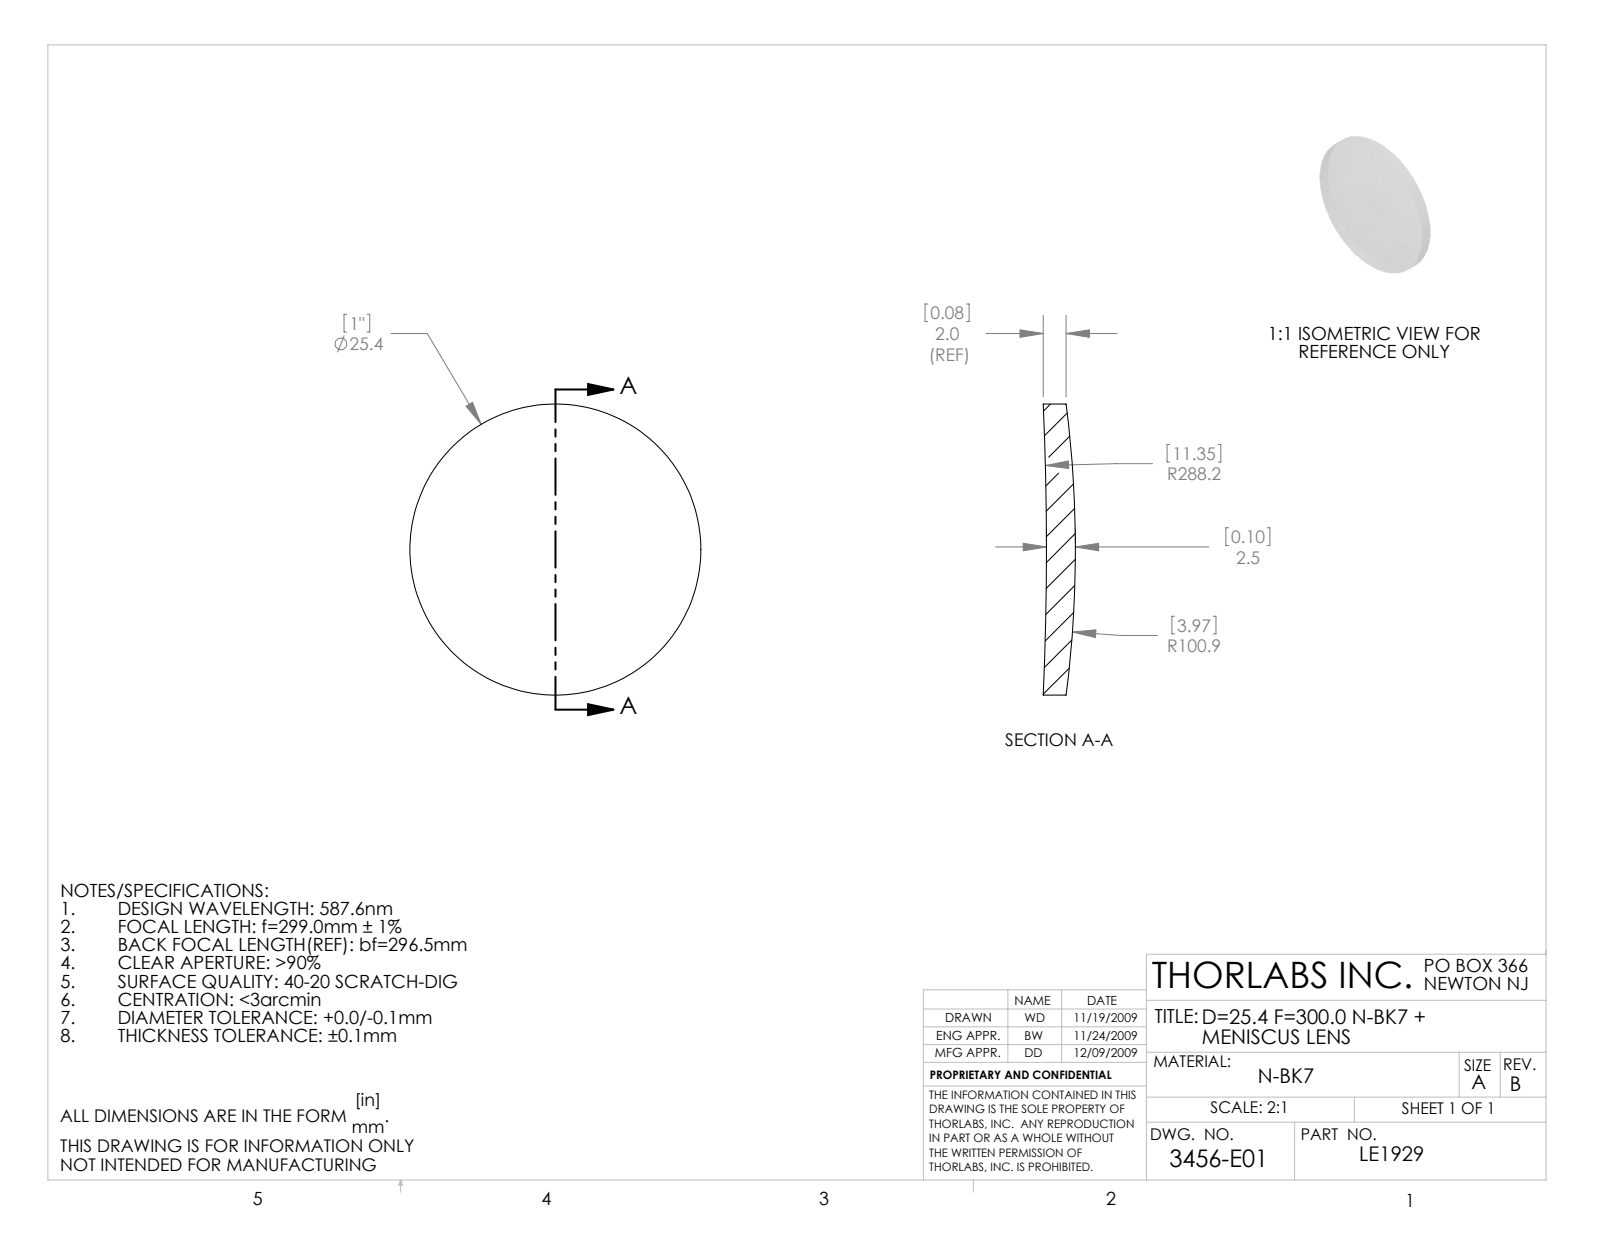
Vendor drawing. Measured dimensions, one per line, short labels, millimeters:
name: 3456-E0W
written by: SolidWorks 2009 (AUTOMOTIVE_DESIGN)
unit: mm
bodies: 1 solid, 6 faces (0 planar, 2 cylindrical, 4 other)
size: 25.4 × 25.4 × 2.8
volume: 1 145 mm³; area: 1 175 mm²
bosses: 1× ⌀25.4
